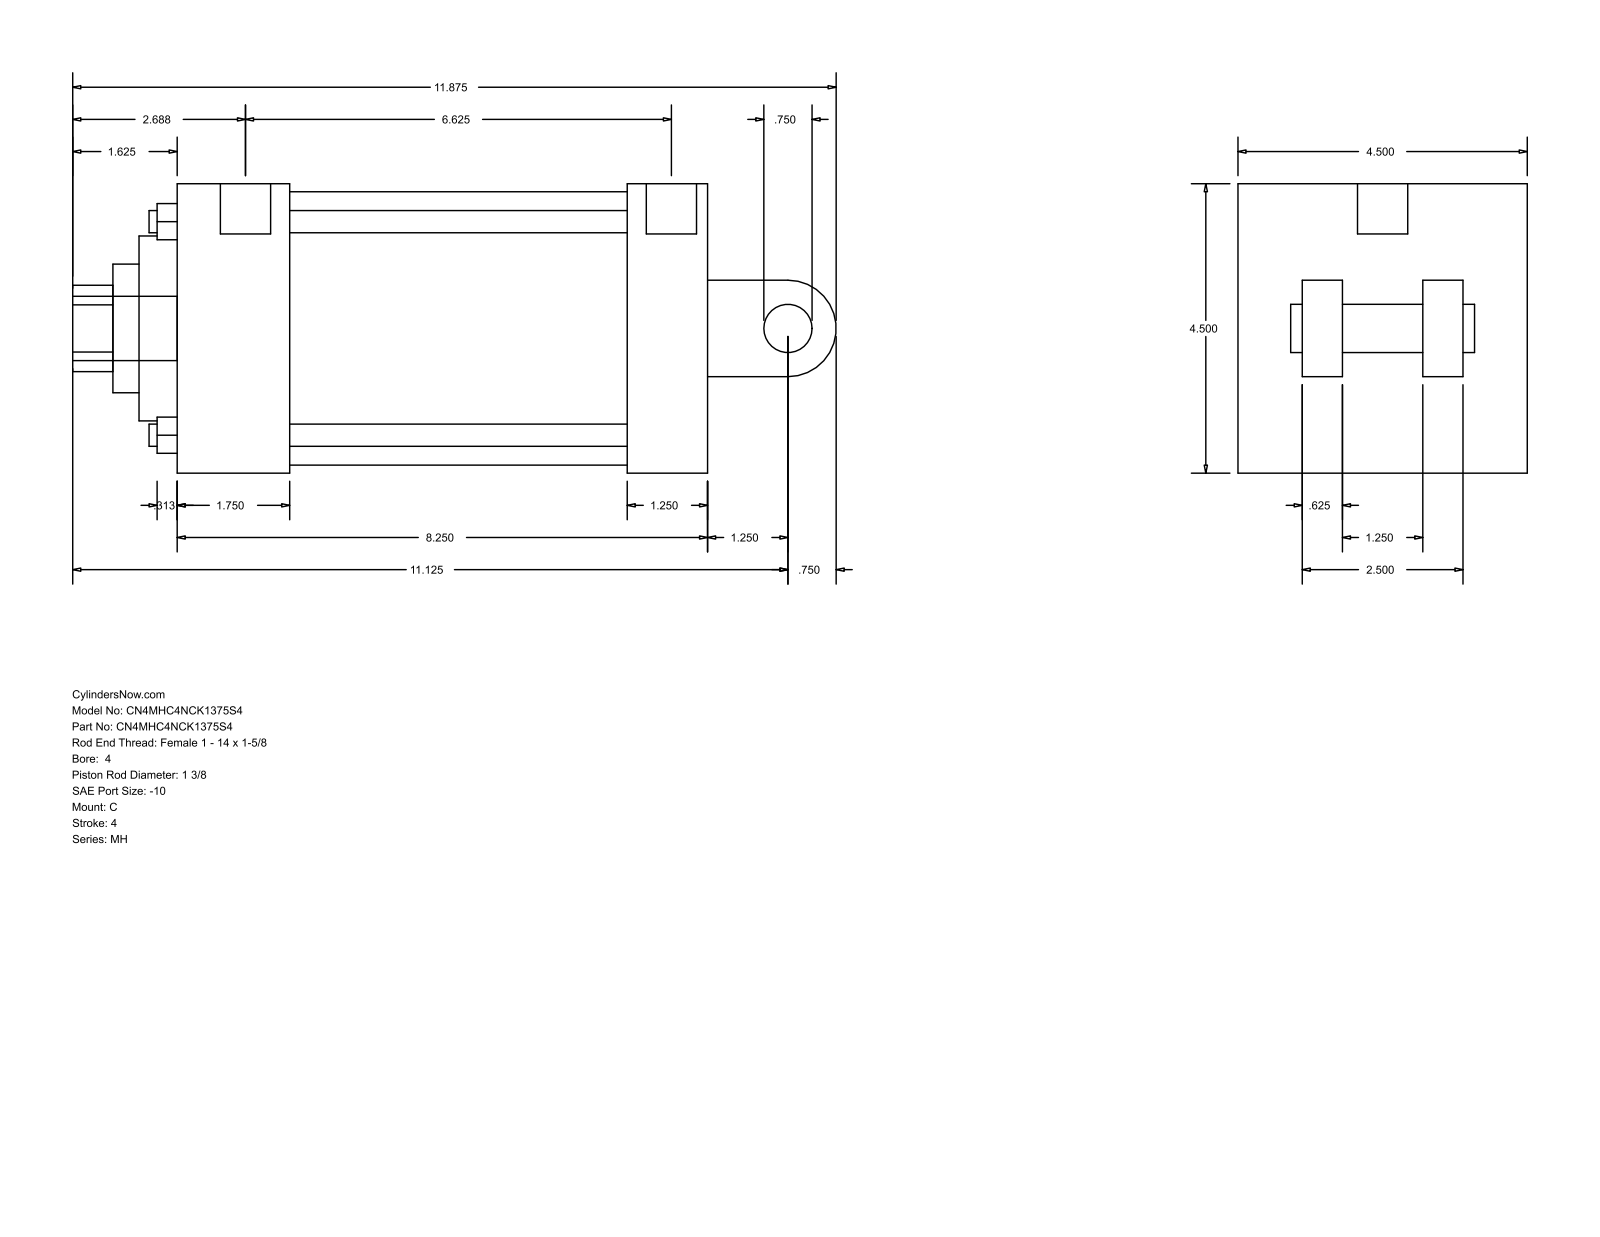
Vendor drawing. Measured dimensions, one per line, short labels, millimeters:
name: MH_C__0400_1.375
written by: GSSL Pune (CONFIG_CONTROL_DESIGN)
unit: mm
bodies: 0 solids, 101 faces (71 planar, 30 cylindrical, 0 other)
size: 301.62 × 114.3 × 114.3
holes: 4× ⌀8.76, 2× ⌀8.73, 1× ⌀19.84, 1× ⌀34.92, 1× ⌀50.8, 1× ⌀73.03, 1× ⌀107.95
bosses: 2× ⌀8.73, 1× ⌀25.4, 1× ⌀19.84, 1× ⌀19.05
rounds: 1× R17.06, 1× R19.05
face distances: 114.3, 209.55, 44.45, 177.8, 133.35, 165.1, 31.75, 73.03, 41.27, 38.1
hole spacings: 59.62, 84.32, 119.25, 1.58
